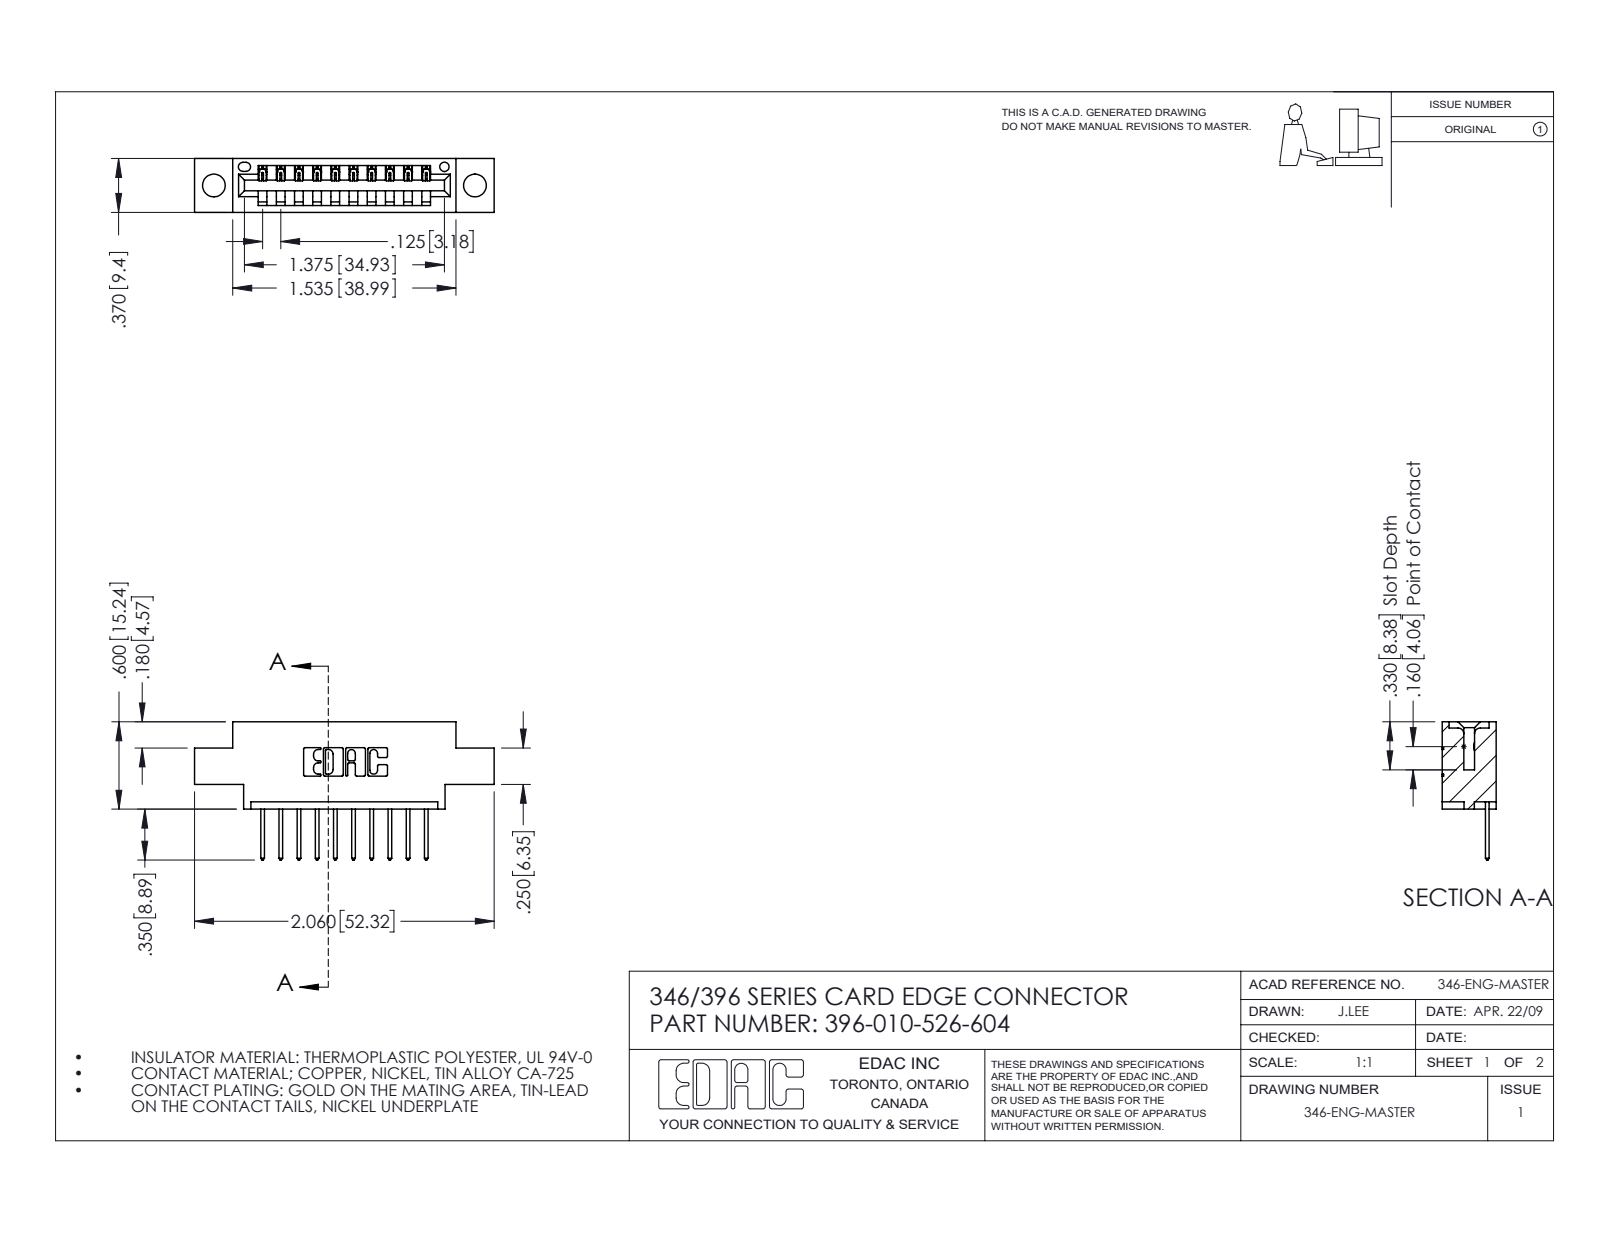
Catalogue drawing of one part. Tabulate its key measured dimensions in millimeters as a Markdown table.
| quantity | value |
| --- | --- |
| part name | 396-010-526-604; 346 Part_0.170 Offset - 0.156 Dia-TH; 345-292-001_345-293-126 |
| STEP written by | SolidWorks 2016 (CONFIG_CONTROL_DESIGN) |
| units | millimeters |
| bodies | 11 solids, 706 faces (480 planar, 226 cylindrical, 0 other) |
| overall size | 52.3 × 24.1 × 9.4 |
| volume | 4 540 mm³ |
| surface area | 5 282 mm² |
| round holes (diameter × count) | 4 × 2, 1.6 × 1 |
| partial cylindrical surfaces (radius × count) | 0.3 × 22, 0.2 × 20, 0.3 × 20, 0.2 × 6, 0.8 × 6, 0.7 × 3, 0.8 × 2, 1 × 2 |
| main face-to-face distances | 6.4, 9.4, 1.2, 8.2, 1.8, 7.6, 0.6, 3.8, 5.6, 2.5 |
| hole center spacings | 6.2, 40.4, 45.6 |
